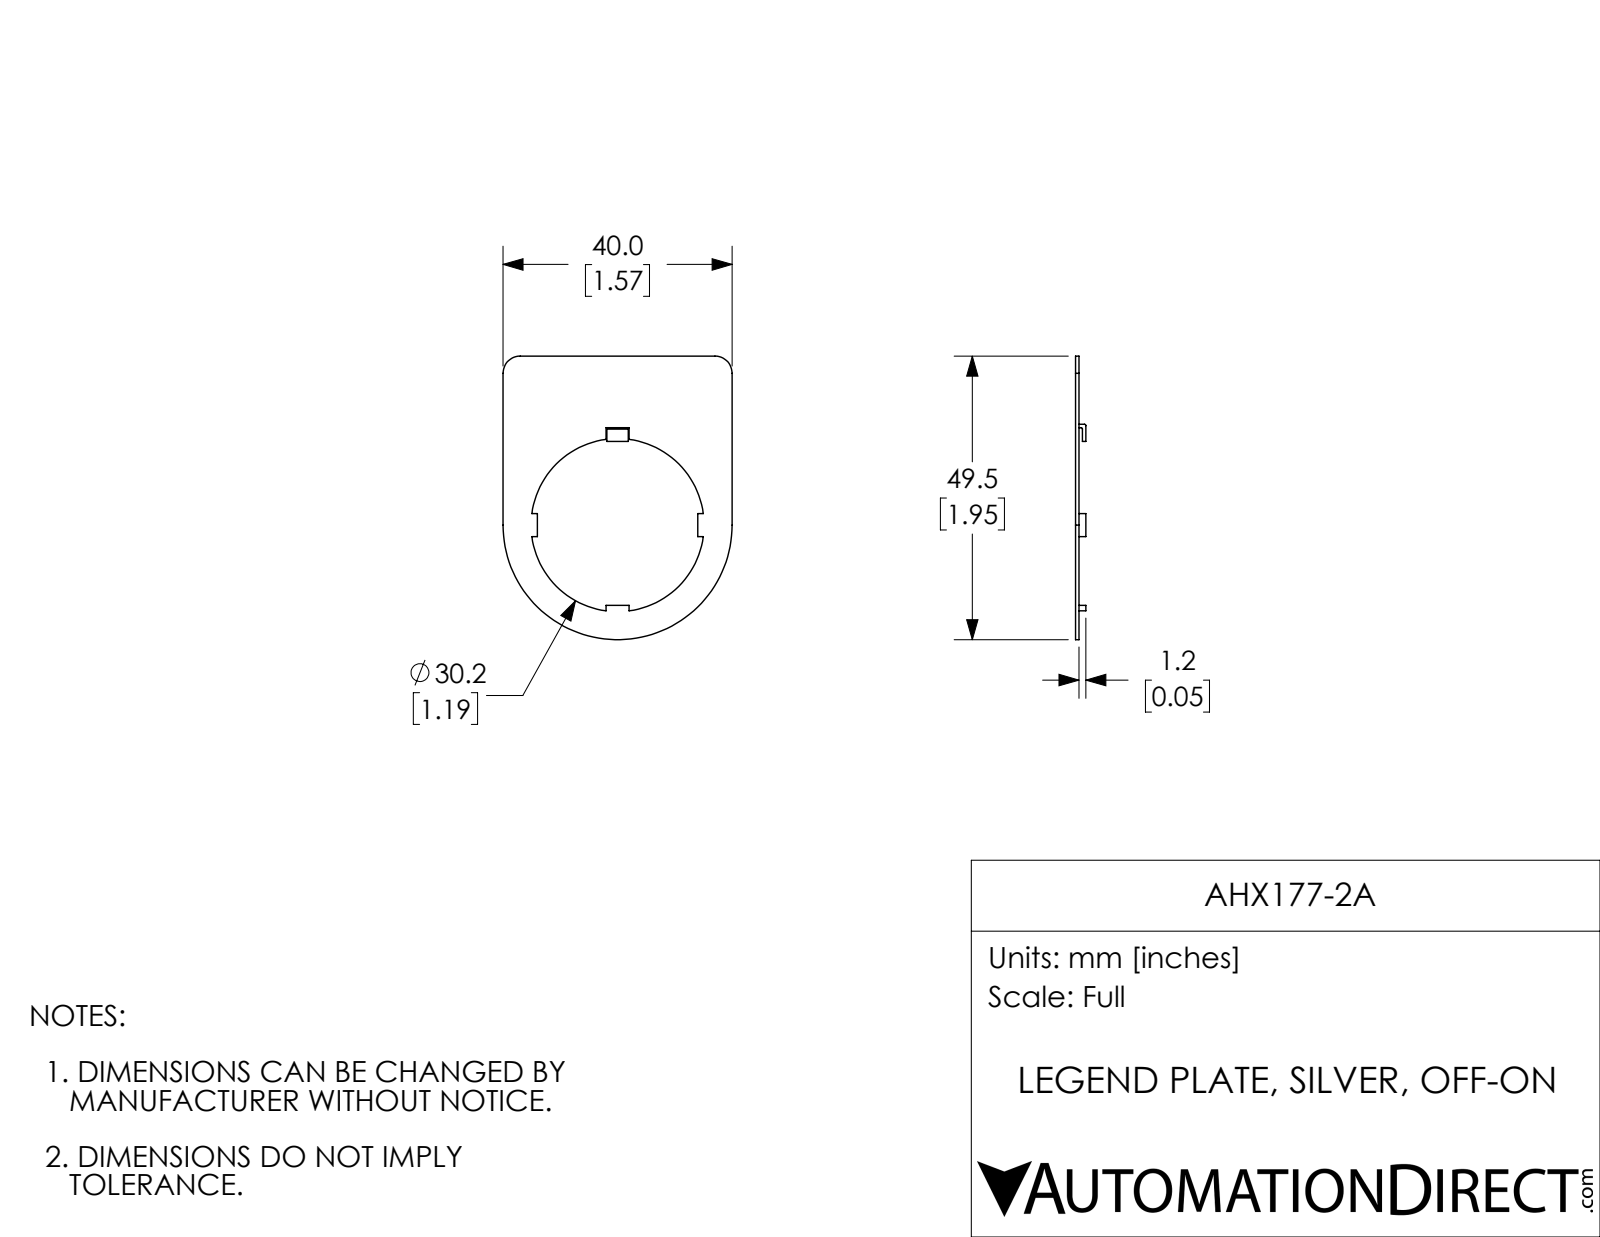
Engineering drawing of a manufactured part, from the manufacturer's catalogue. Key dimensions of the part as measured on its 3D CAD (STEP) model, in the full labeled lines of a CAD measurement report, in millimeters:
Part name (STEP PRODUCT): AHX177-2A
STEP written by: SolidWorks 2017 (AUTOMOTIVE_DESIGN)
Units: millimetres
Bodies: 1 solid, 38 faces (29 planar, 9 cylindrical, 0 other)
Overall size (bounding box): 49.5 × 40 × 1.8
Volume: 670 mm³ · Surface area: 2 410 mm²
Round holes (diameter × count): ⌀30.2 ×1
Partial cylindrical surfaces — rounded edges, fillets, slot ends (radius × count): R0.3 ×2, R3 ×2, R20 ×1
Main face-to-face distances: 0.6, 1.2, 1.8, 40, 1, 6, 34, 5, 35, 29
